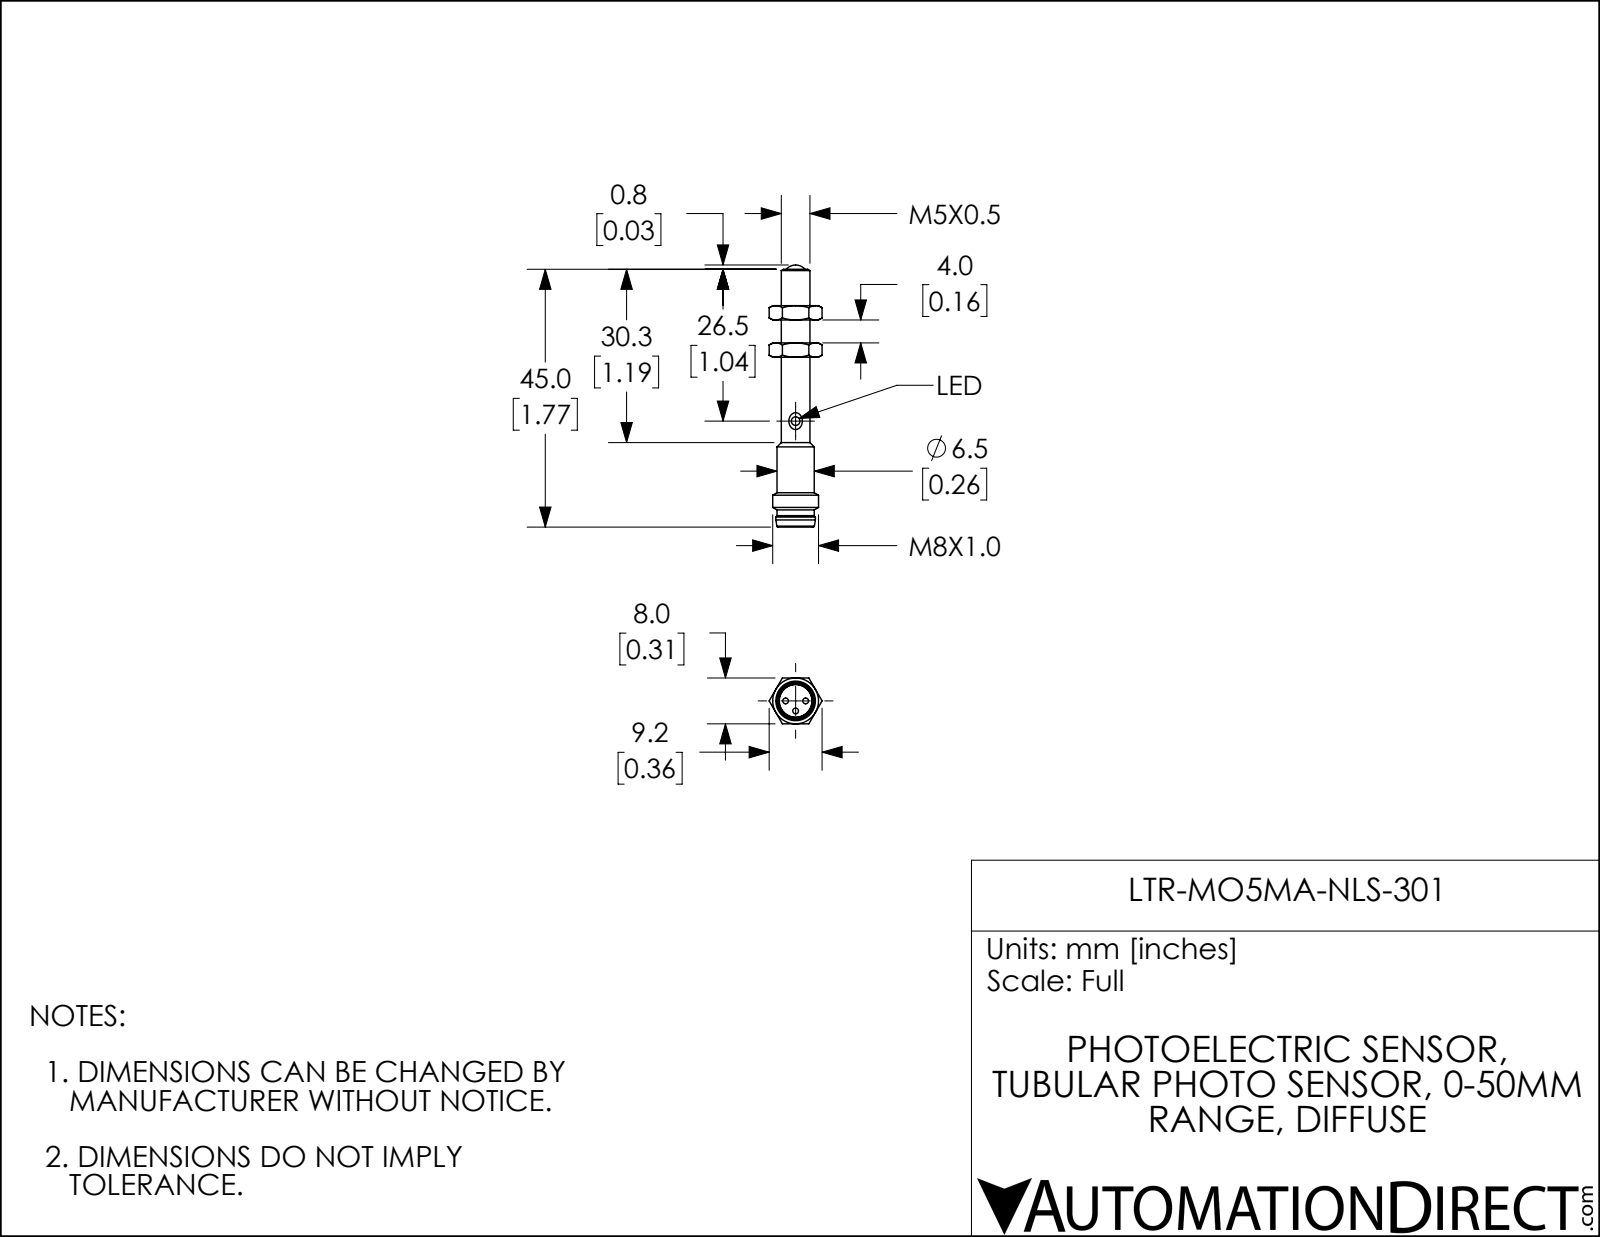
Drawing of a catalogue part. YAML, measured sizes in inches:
part_name: "LxR-M05MA-NxS"
step_written_by: "SolidWorks 2018 (AUTOMOTIVE_DESIGN)"
units: inches
bodies: {solids: 1, faces: 30, planar: 4, cylindrical: 13, other: 13}
overall_size: [1.801, 0.315, 0.315]
volume: 0.062
surface_area: 1.552
round_holes:
  - {diameter: 0.059, count: 1}
  - {diameter: 0.228, count: 1}
round_bosses_or_shafts:
  - {diameter: 0.039, count: 3}
  - {diameter: 0.315, count: 1}
  - {diameter: 0.272, count: 1}
  - {diameter: 0.256, count: 1}
  - {diameter: 0.224, count: 1}
  - {diameter: 0.197, count: 1}
partial_cylinders:
  - {radius: 0.07, count: 1}
face_to_face_distances: [1.578, 0.193, 1.772, 0.197, 1.575]
